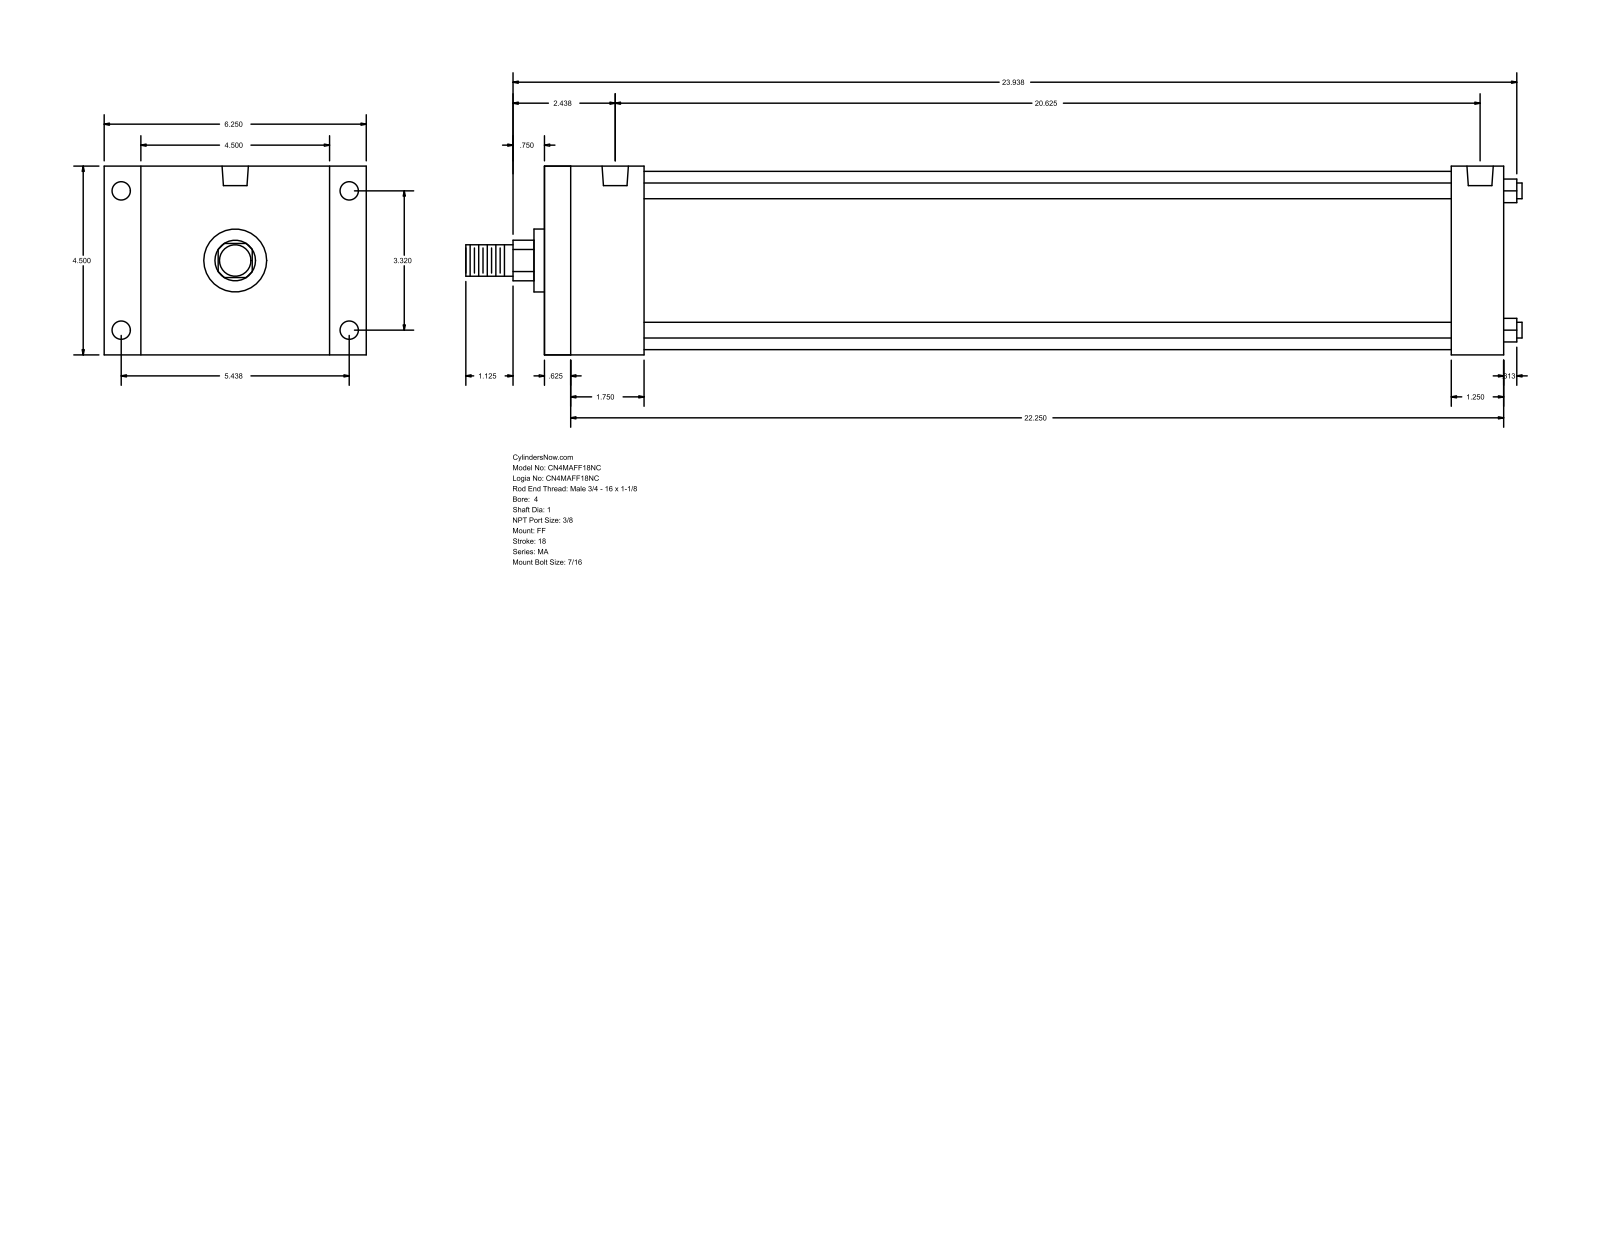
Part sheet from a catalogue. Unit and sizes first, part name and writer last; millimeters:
Units: millimetres
Overall size (bounding box): 639.76 × 158.75 × 114.3
Round holes (diameter × count): ⌀11.11 ×8, ⌀15.93 ×2
Round bosses / shafts (diameter × count): ⌀9.53 ×4, ⌀107.95 ×1, ⌀38.1 ×1, ⌀25.4 ×1, ⌀19.05 ×1
Partial cylindrical surfaces — rounded edges, fillets, slot ends (radius × count): R12.29 ×1
Main face-to-face distances: 114.3, 581.03, 15.87, 565.16, 22.23, 136.53, 549.28, 533.41, 31.75, 60.33
Hole centre spacings: 84.32, 138.12, 161.82, 514.35, 4.76, 4.77, 519.11, 519.12
Bodies: 0 solids, 92 faces (64 planar, 28 cylindrical, 0 other)
Part name (STEP PRODUCT): MA_FF__0400_1
STEP written by: GSSL Pune (CONFIG_CONTROL_DESIGN)
